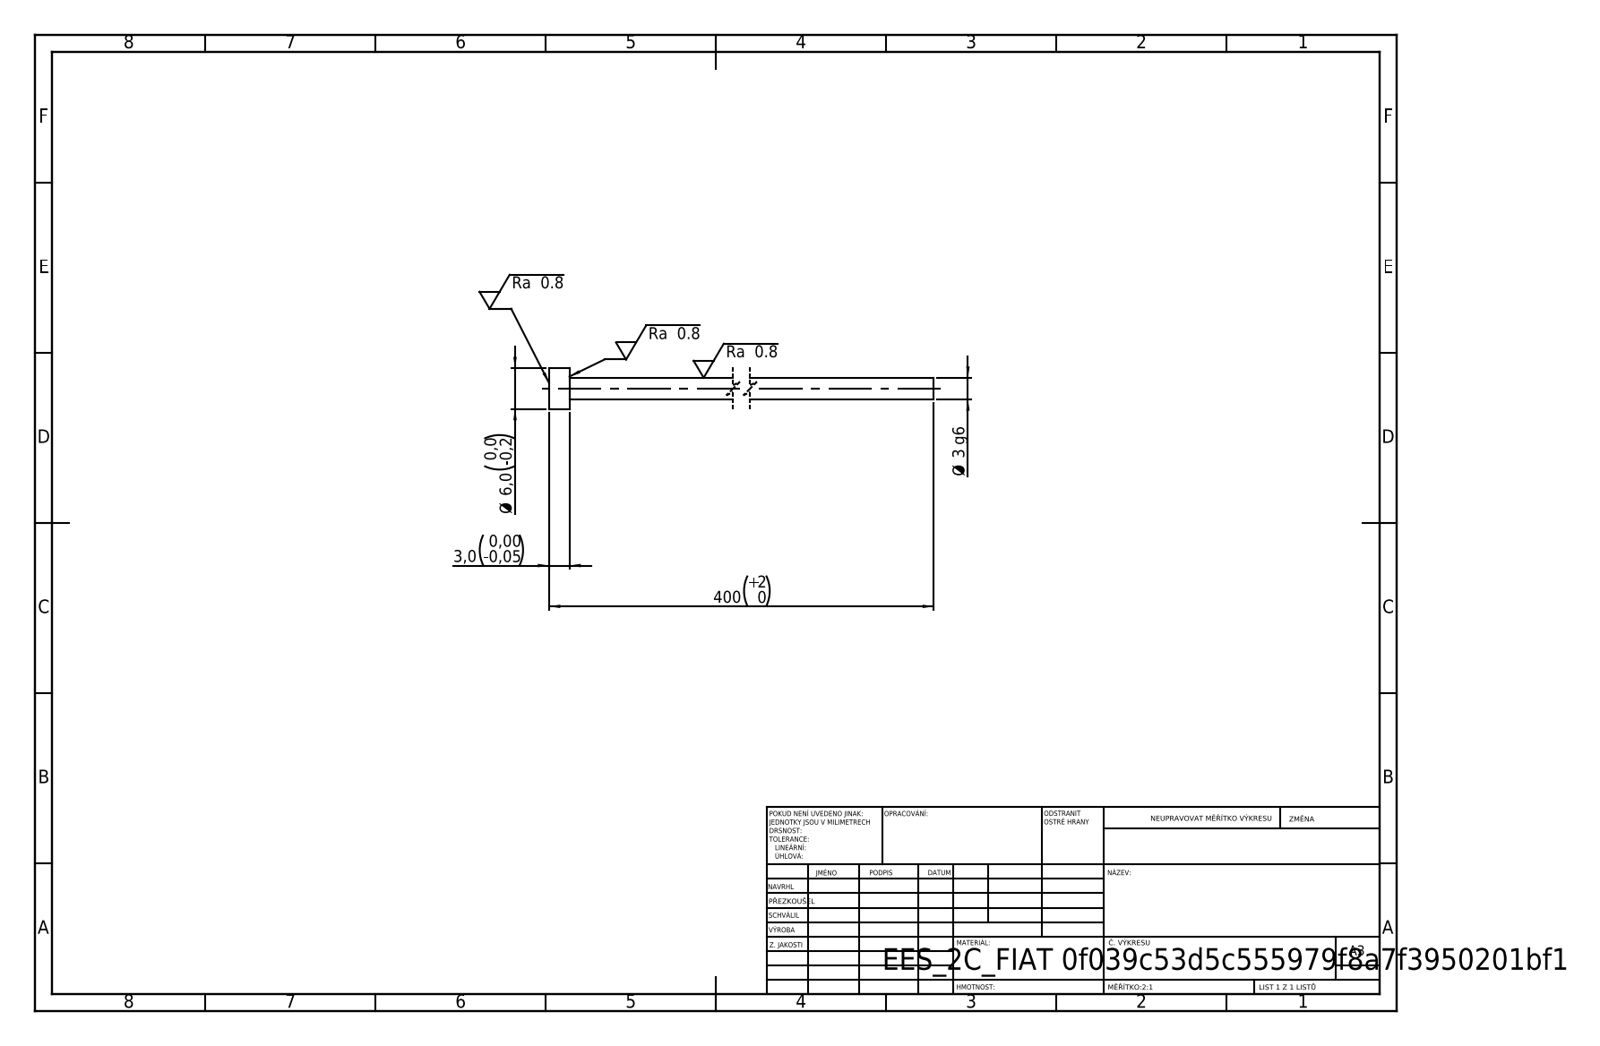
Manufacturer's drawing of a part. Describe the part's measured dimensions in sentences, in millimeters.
Its 3-D file was written by "SolidWorks 2019 (CONFIG_CONTROL_DESIGN)". It is 1 solid with 7 faces: 3 planar, 4 cylindrical and 0 other. Overall it measures 400 by 6 by 6 millimeters. Its volume is 3 278 cubic millimeters and its surface area 4 104 square millimeters. Round bosses or shafts: 1 of diameter 6, 1 of diameter 3.2. The main face-to-face distances are 3, 400, 397.
